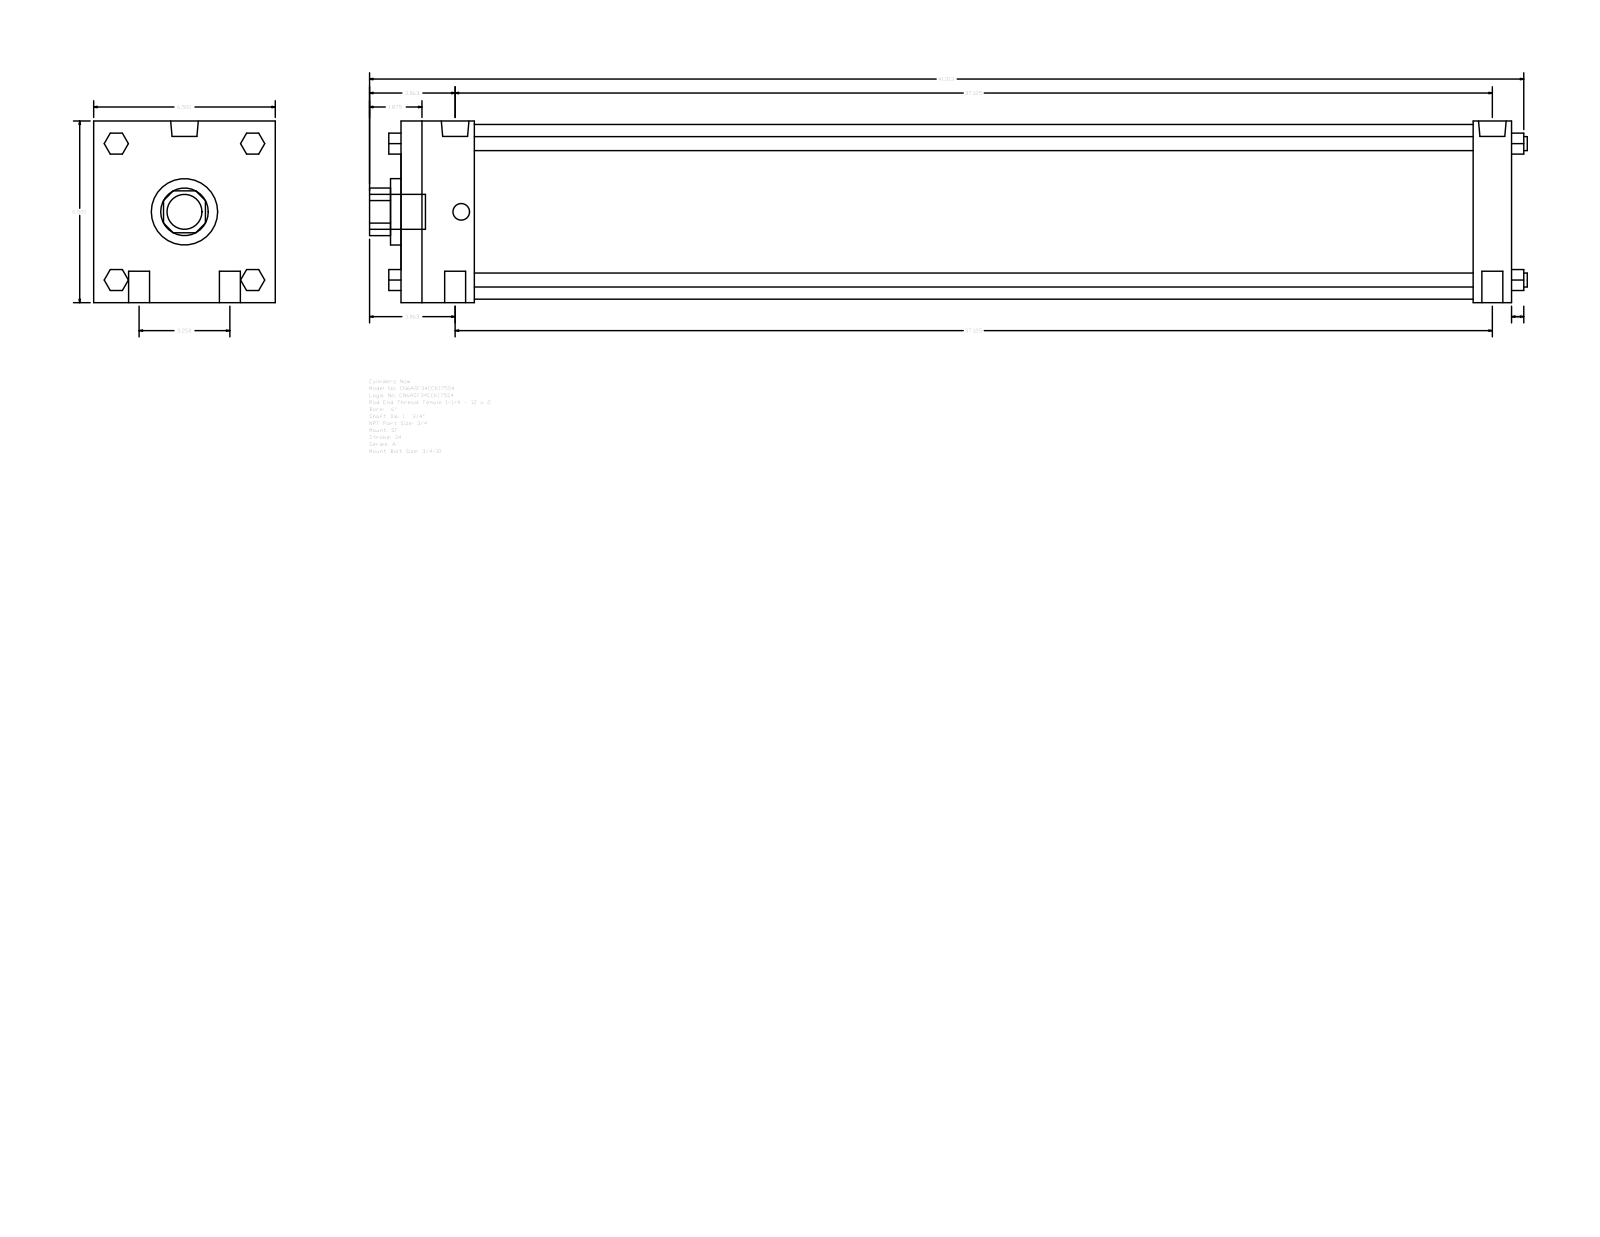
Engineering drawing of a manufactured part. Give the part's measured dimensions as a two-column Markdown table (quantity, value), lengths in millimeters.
| quantity | value |
| --- | --- |
| part name | A_SF__0600_1.75 |
| STEP written by | GSSL Pune (CONFIG_CONTROL_DESIGN) |
| units | millimeters |
| bodies | 0 solids, 124 faces (94 planar, 30 cylindrical, 0 other) |
| overall size | 1052.51 × 165.1 × 165.1 |
| round holes (diameter × count) | 44.45 × 1, 60.33 × 1, 158.75 × 1 |
| round bosses / shafts (diameter × count) | 19.05 × 4, 12.7 × 4, 25.12 × 2, 15.08 × 2, 31.75 × 1 |
| partial cylindrical surfaces (radius × count) | 21.63 × 1 |
| main face-to-face distances | 165.1, 1009.65, 34.92, 974.73, 66.68, 908.05, 942.97, 19.05, 61.97, 107.34 |
